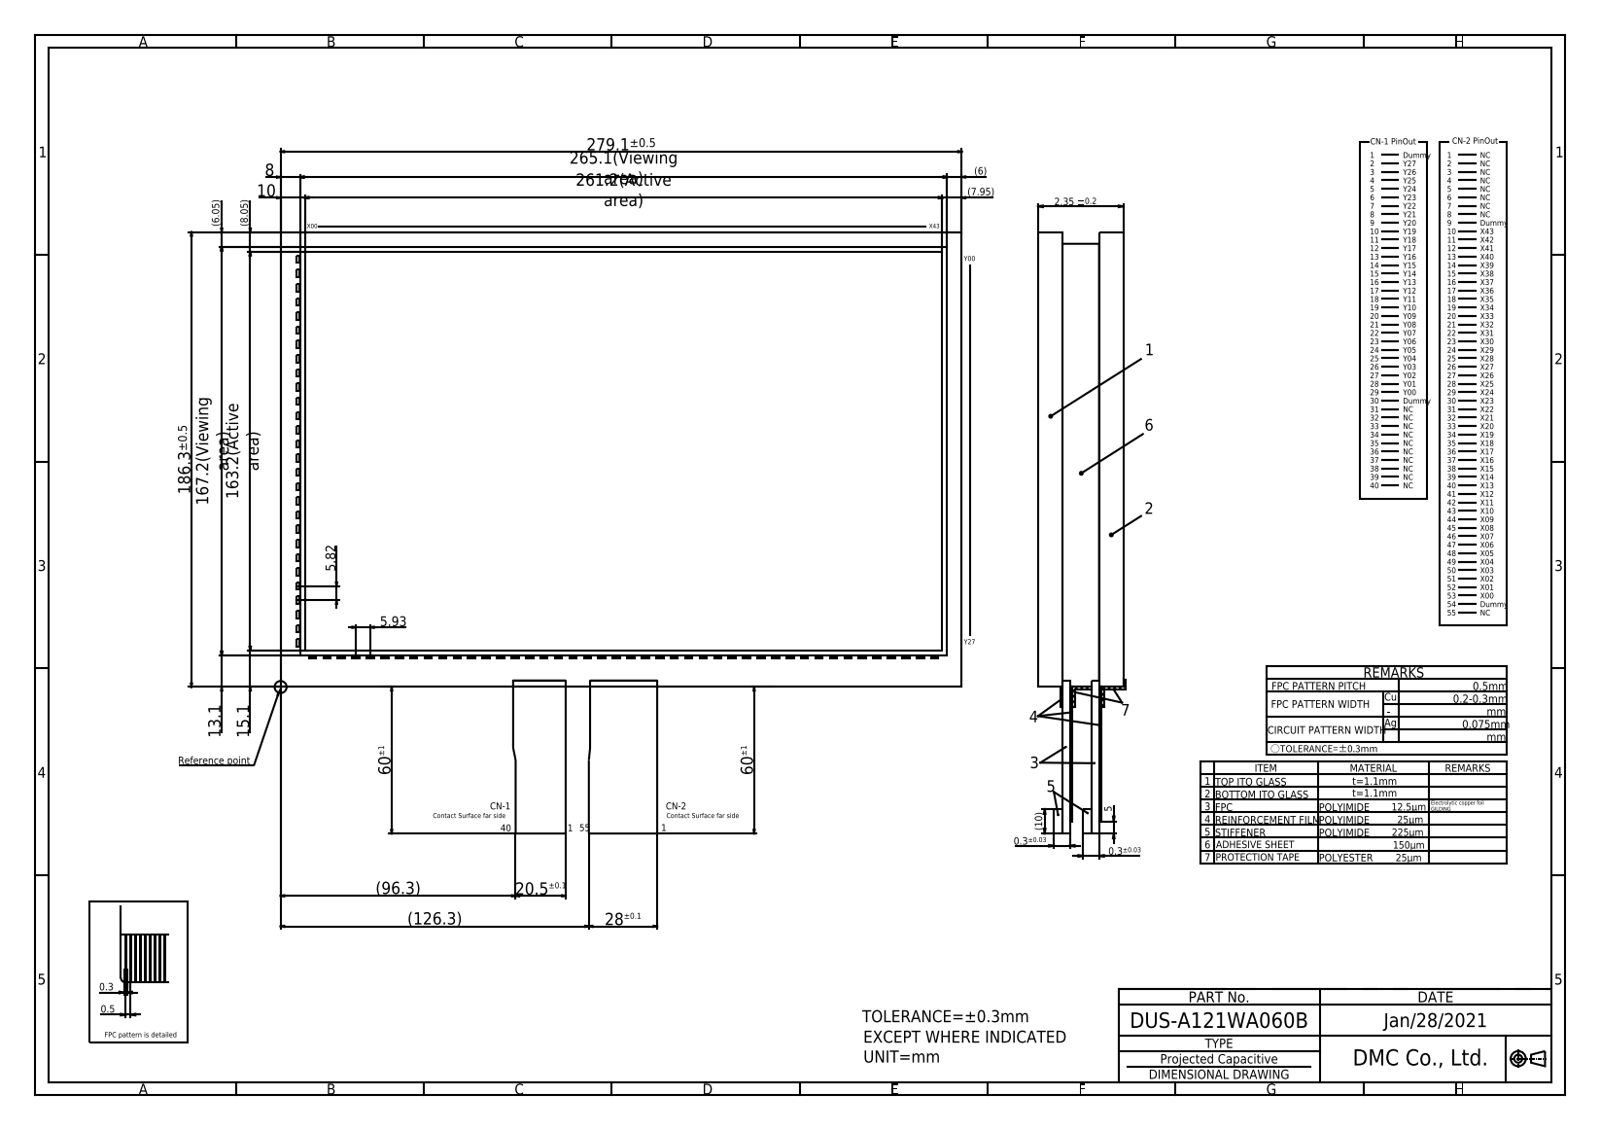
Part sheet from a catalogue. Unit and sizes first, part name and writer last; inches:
Units: inches
Overall size (bounding box): 15.383 × 11.164 × 0.093
Partial cylindrical surfaces — rounded edges, fillets, slot ends (radius × count): R0.008 ×4
Main face-to-face distances: 0.093, 0.043, 0.045, 0.047, 0.049, 0.039, 0.089, 7.335, 0.031, 0.028
Volume: 7.471 in³ · Surface area: 174 in²
Bodies: 1 solid, 422 faces (418 planar, 4 cylindrical, 0 other)
Part name (STEP PRODUCT): DUS-A121WA060B
STEP written by: Autodesk Inventor 2020 (CONFIG_CONTROL_DESIGN)
